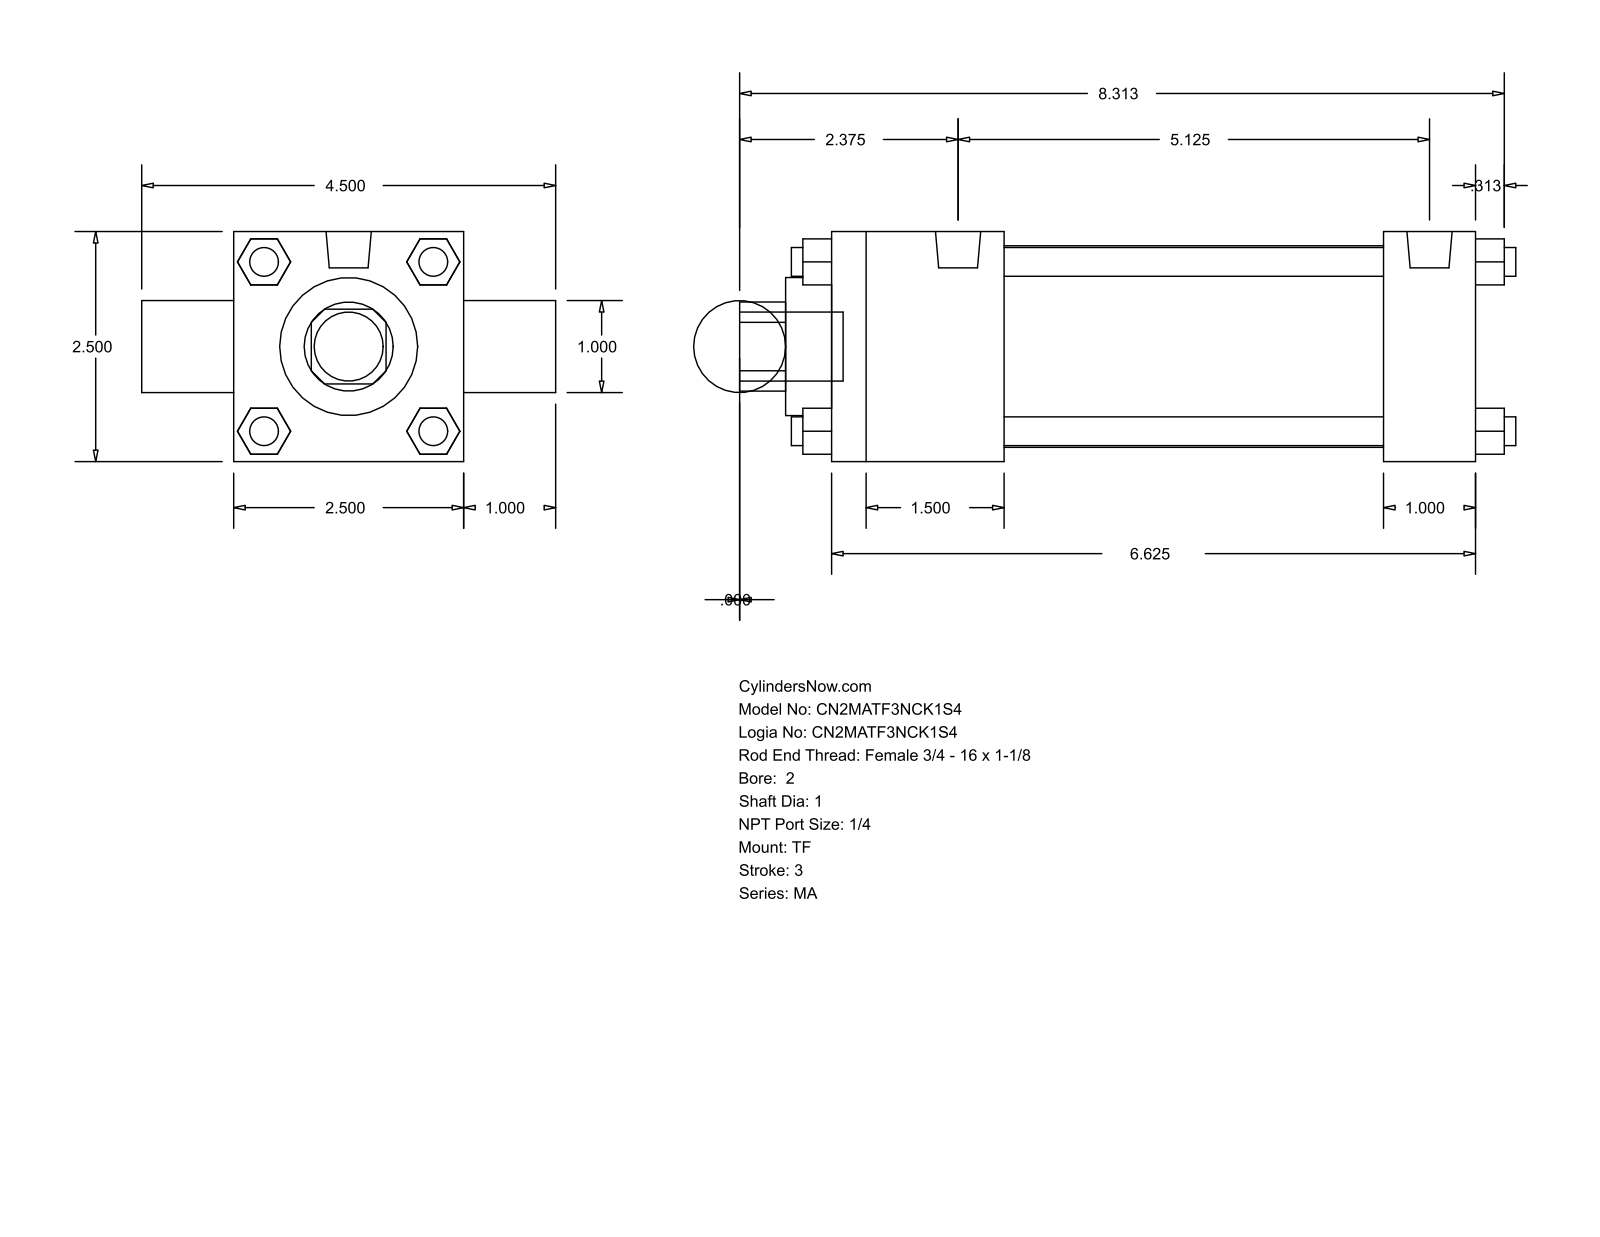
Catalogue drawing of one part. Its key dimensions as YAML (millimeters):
part_name: "MA_TF__0200_1"
step_written_by: "GSSL Pune (CONFIG_CONTROL_DESIGN)"
units: millimeters
bodies: {solids: 0, faces: 120, planar: 92, cylindrical: 28, other: 0}
overall_size: [214.31, 114.3, 63.5]
round_holes:
  - {diameter: 25.4, count: 2}
  - {diameter: 38.1, count: 1}
  - {diameter: 55.63, count: 1}
round_bosses_or_shafts:
  - {diameter: 7.94, count: 7}
  - {diameter: 12.49, count: 2}
  - {diameter: 19.05, count: 1}
partial_cylinders:
  - {radius: 12.29, count: 1}
face_to_face_distances: [63.5, 25.4, 177.8, 12.7, 47.63, 152.4, 104.77, 130.17, 88.9, 23.37]
